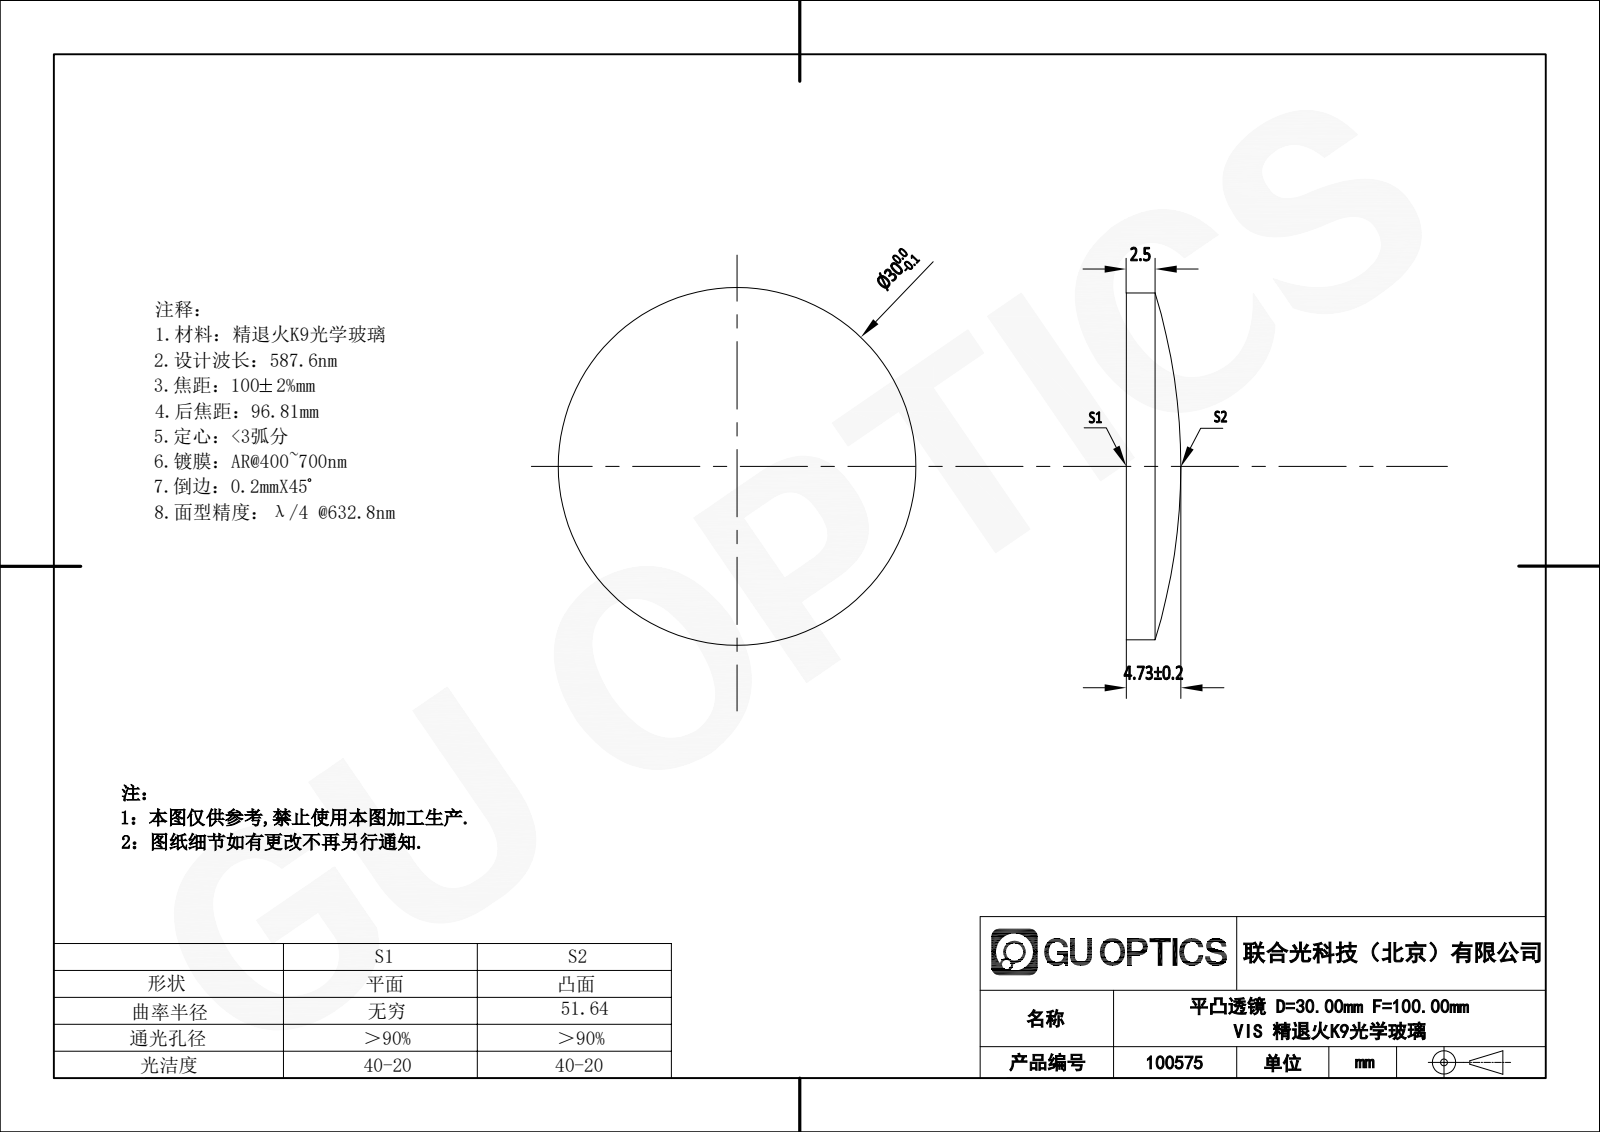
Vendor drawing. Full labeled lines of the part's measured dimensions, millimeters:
Part name (STEP PRODUCT): 100575
STEP written by: SolidWorks 2020 (CONFIG_CONTROL_DESIGN)
Units: millimetres
Bodies: 1 solid, 5 faces (1 planar, 2 cylindrical, 2 other)
Overall size (bounding box): 30 × 30 × 4.73
Volume: 2 561 mm³ · Surface area: 1 665 mm²
Round bosses / shafts (diameter × count): ⌀30 ×1
